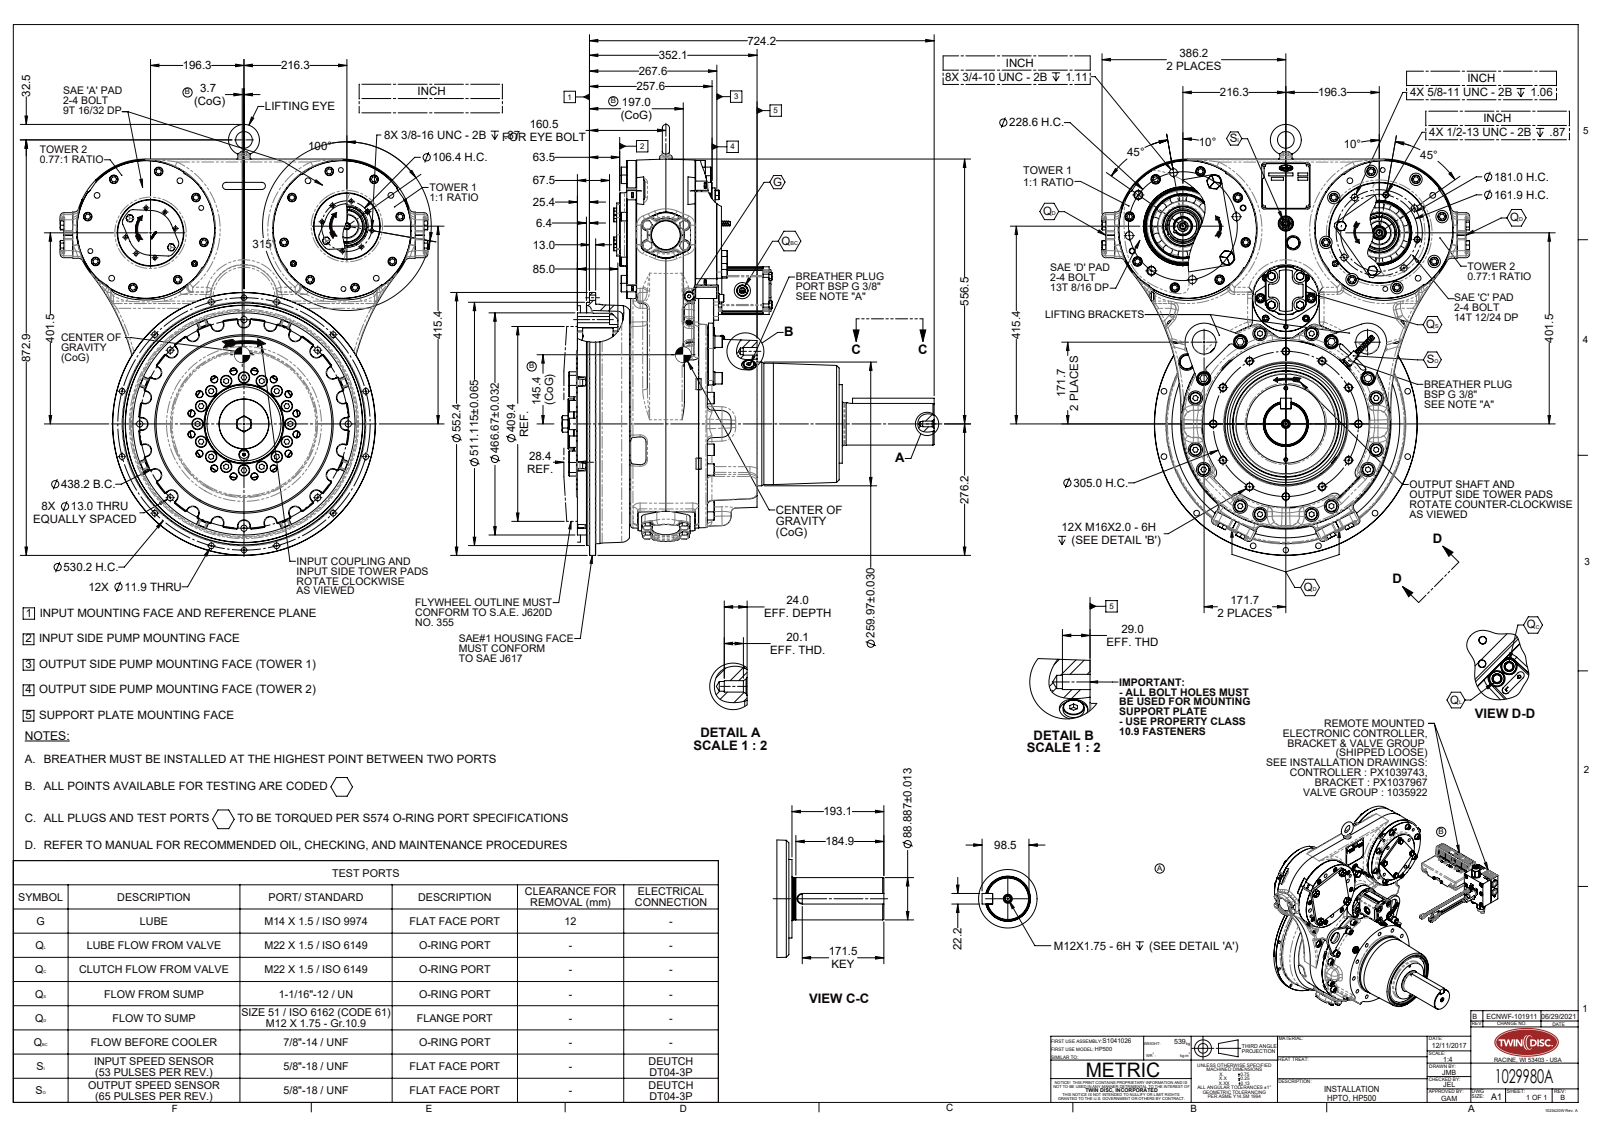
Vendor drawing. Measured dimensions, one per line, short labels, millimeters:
name: 1029980A
written by: SolidWorks 2019 (AUTOMOTIVE_DESIGN)
unit: mm
bodies: 0 solids, 5081 faces (1892 planar, 1695 cylindrical, 1494 other)
size: 905.39 × 781.85 × 772.32
holes: 24× ⌀14, 14× ⌀16, 12× ⌀7.94, 12× ⌀11.91, 12× ⌀30, 8× ⌀13, 8× ⌀20, 8× ⌀26, 7× ⌀12.02, 7× ⌀34, 6× ⌀10.2, 6× ⌀18
bosses: 40× ⌀1.59, 32× ⌀24, 17× ⌀18, 9× ⌀16, 6× ⌀10, 5× ⌀30.23, 4× ⌀28, 3× ⌀140
rounds: 76× R2.54, 51× R5, 37× R1, 36× R10, 28× R12.7, 25× R1.52, 24× R3, 18× R0.5
face distances: 0.6, 7, 130.52, 123.52, 150.52, 151.12, 7.6, 143.52, 129.92, 122.92
hole spacings: 152.5, 78.94, 215.67, 264.14, 294.61, 197.5, 112.5, 305
